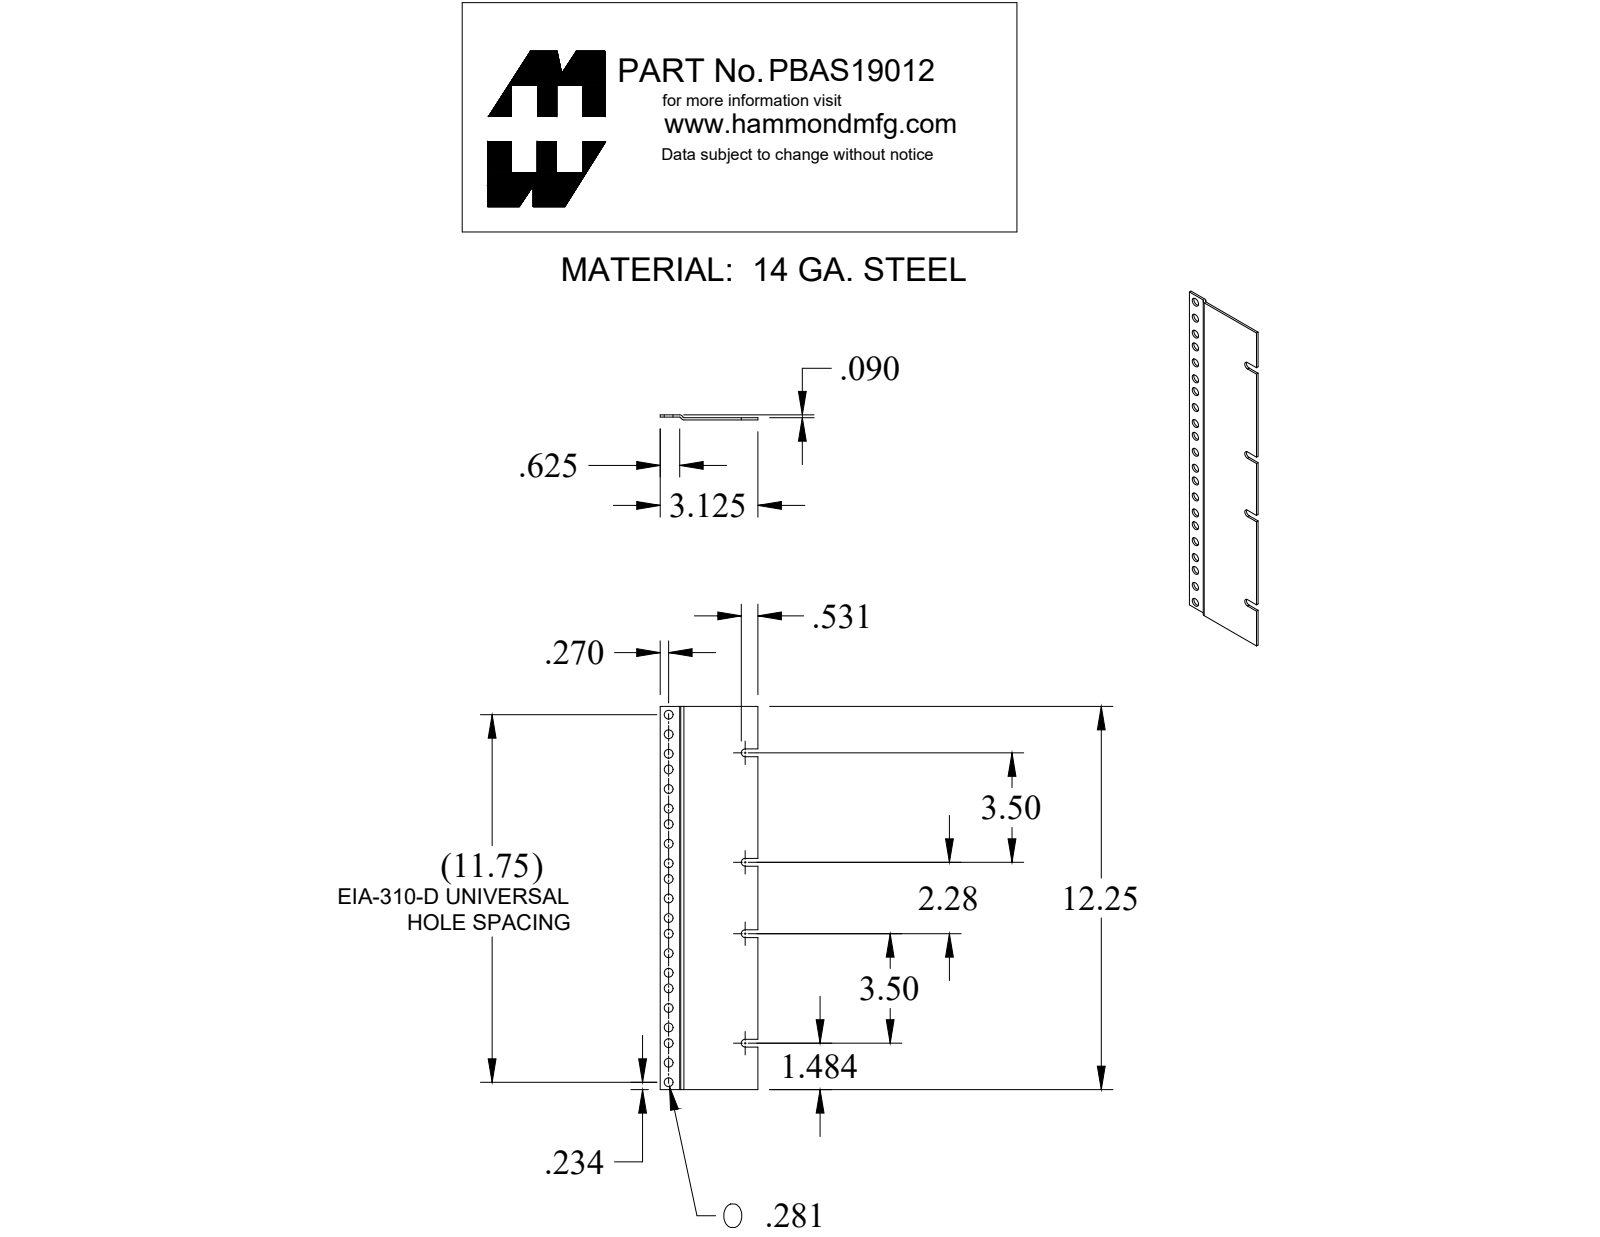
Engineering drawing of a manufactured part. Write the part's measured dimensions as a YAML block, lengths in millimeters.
part_name: "PBAS19012BK2"
step_written_by: "SolidWorks 2019 (CONFIG_CONTROL_DESIGN)"
units: millimeters
bodies: {solids: 1, faces: 49, planar: 20, cylindrical: 29, other: 0}
overall_size: [311.2, 79.4, 4.1]
volume: 43570
surface_area: 50120
round_holes:
  - {diameter: 7.1, count: 21}
partial_cylinders:
  - {radius: 3.2, count: 4}
  - {radius: 0.9, count: 2}
  - {radius: 2.7, count: 2}
face_to_face_distances: [1.8, 2.3, 4.1, 0.5, 2.3, 1.8, 79.4, 311.2, 88.9, 6.4]
hole_center_spacings: [44.5, 88.9, 133.4, 177.8, 15.9, 15.9, 31.8, 12.7]
